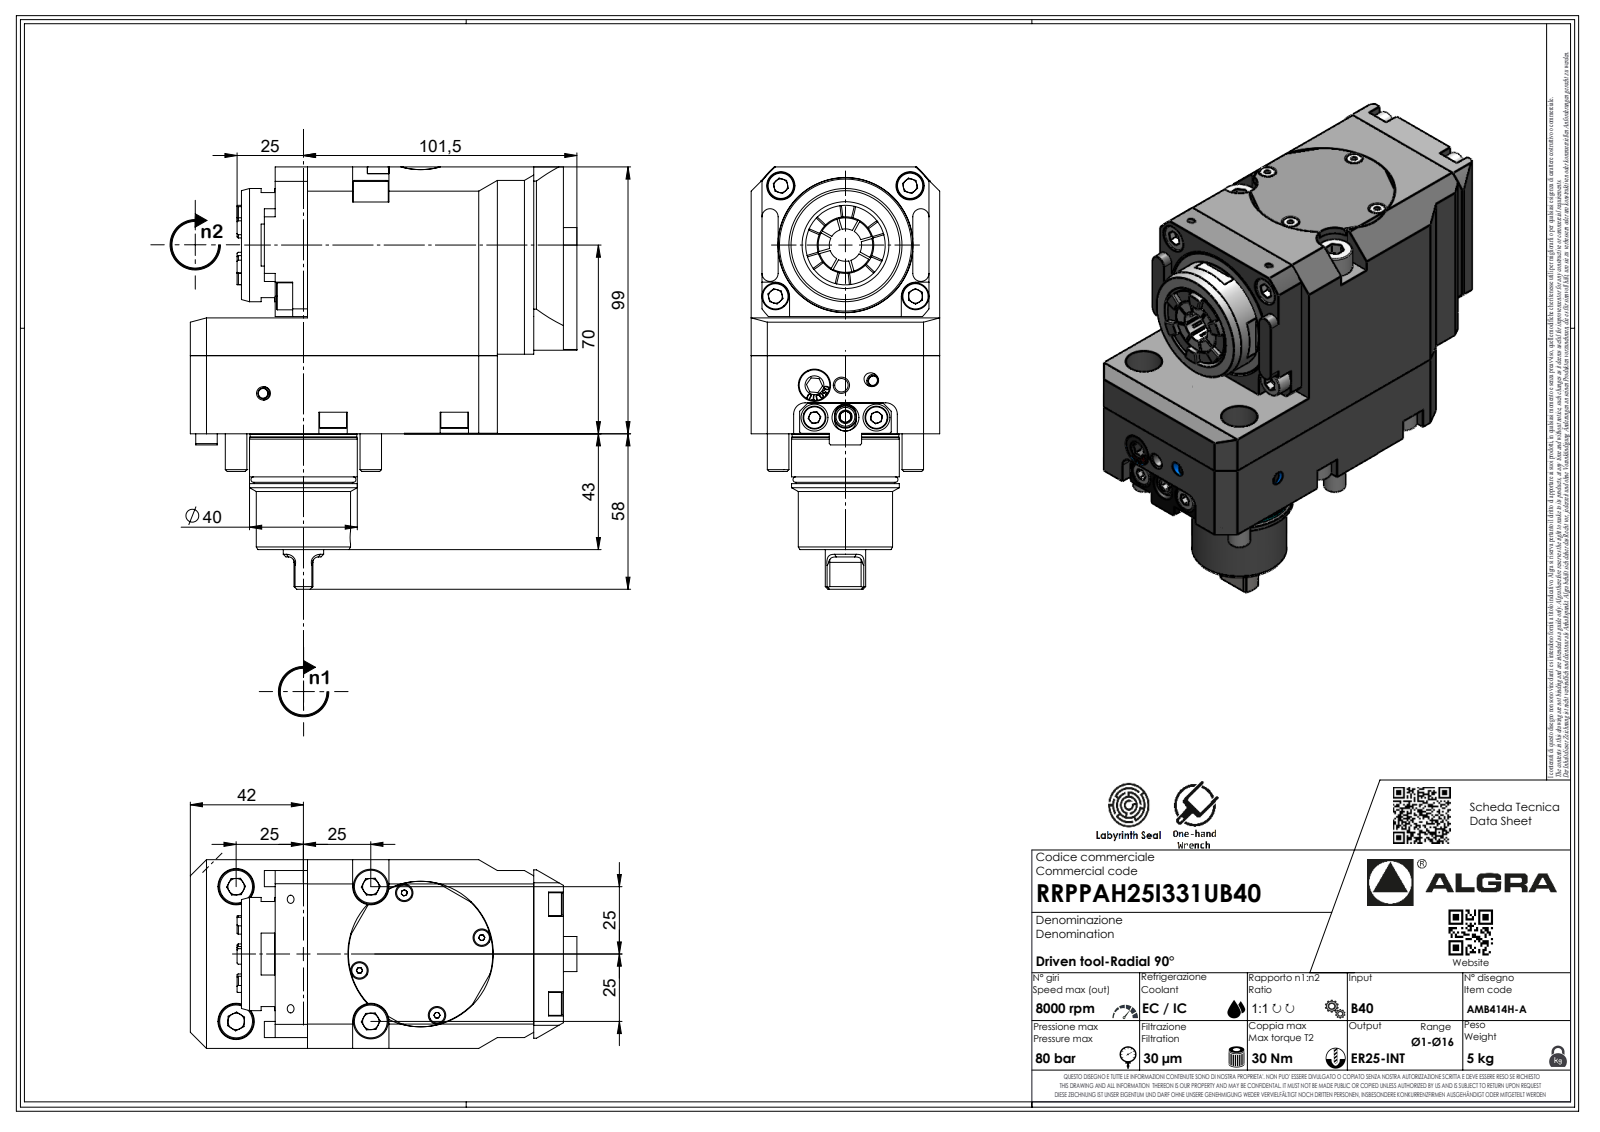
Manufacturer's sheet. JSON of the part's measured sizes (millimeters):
{"part_name": "RRPPAH25I331UB40", "step_written_by": "SolidWorks 2023 (AUTOMOTIVE_DESIGN)", "units": "millimeters", "bodies": {"solids": 1, "faces": 509, "planar": 332, "cylindrical": 64, "other": 113}, "overall_size": [156.7, 143.5, 70], "volume_mm3": 818610, "surface_area_mm2": 65601, "round_holes": [[2.1, 1]], "round_bosses_or_shafts": [[8, 4], [13, 2], [42, 1], [40, 1], [39.6, 1], [36.4, 1], [35, 1], [15, 1]], "partial_cylinders_radius": [[0.33, 7], [0.52, 7], [3.7, 7], [2, 6], [3, 4], [6.75, 2], [0.21, 1], [6.5, 1]], "face_to_face_distances": [70, 99, 43, 4, 24.5, 56, 66, 138.5, 42.8, 98.8]}
